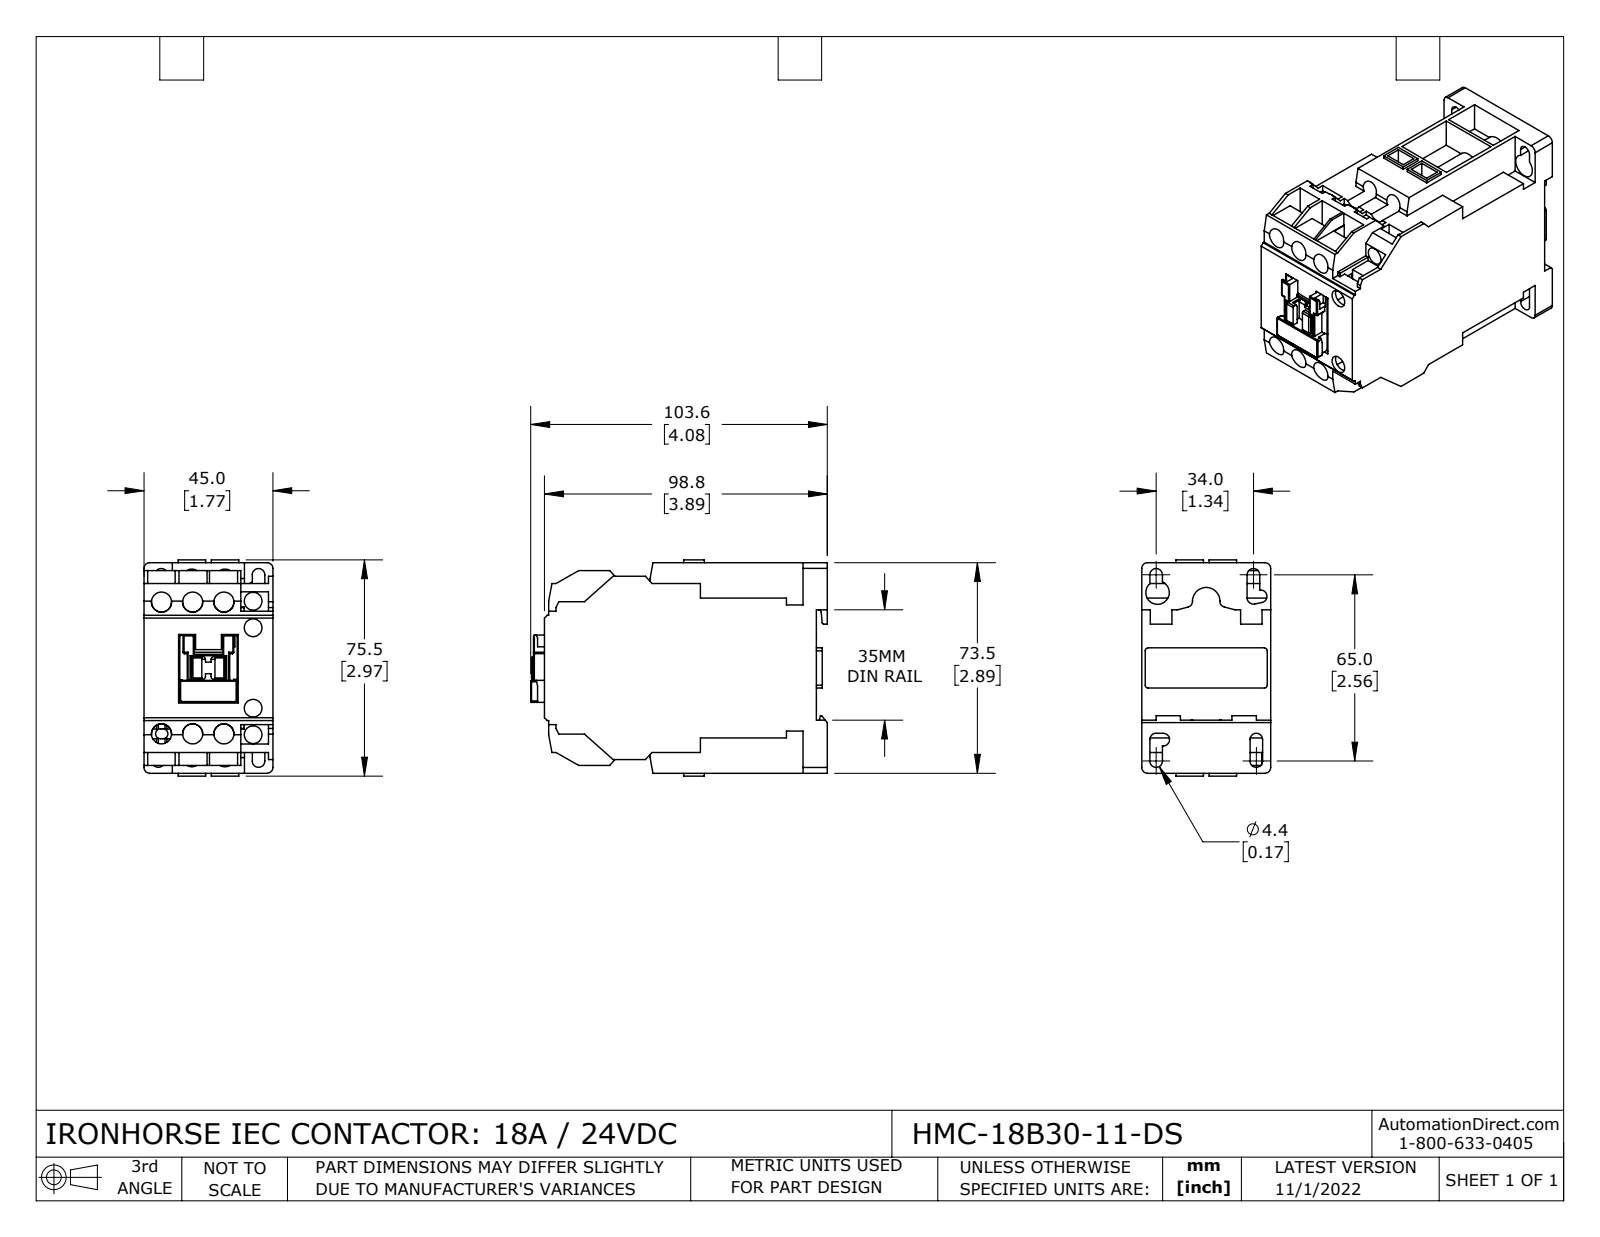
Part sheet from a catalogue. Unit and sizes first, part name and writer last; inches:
Units: inches
Overall size (bounding box): 4.079 × 2.972 × 1.772
Round holes (diameter × count): ⌀0.276 ×6, ⌀0.244 ×4, ⌀0.256 ×4, ⌀0.323 ×1
Partial cylindrical surfaces — rounded edges, fillets, slot ends (radius × count): R0.02 ×22, R0.012 ×13, R0.039 ×13, R0.087 ×9, R0.079 ×8, R0.069 ×2, R0.063 ×1, R0.118 ×1
Main face-to-face distances: 1.772, 0.39, 1.382, 0.429, 0.406, 0.063, 0.201, 2.488, 0.051, 0.285
Hole centre spacings: 0.325, 0.429, 1.861, 2.136, 1.811, 0.364, 0.402, 0.457
Volume: 14.58 in³ · Surface area: 70.35 in²
Bodies: 4 solids, 699 faces (538 planar, 129 cylindrical, 32 other)
Part name (STEP PRODUCT): HMC-18B30-11-DS
STEP written by: SolidWorks 2021 (CONFIG_CONTROL_DESIGN)
